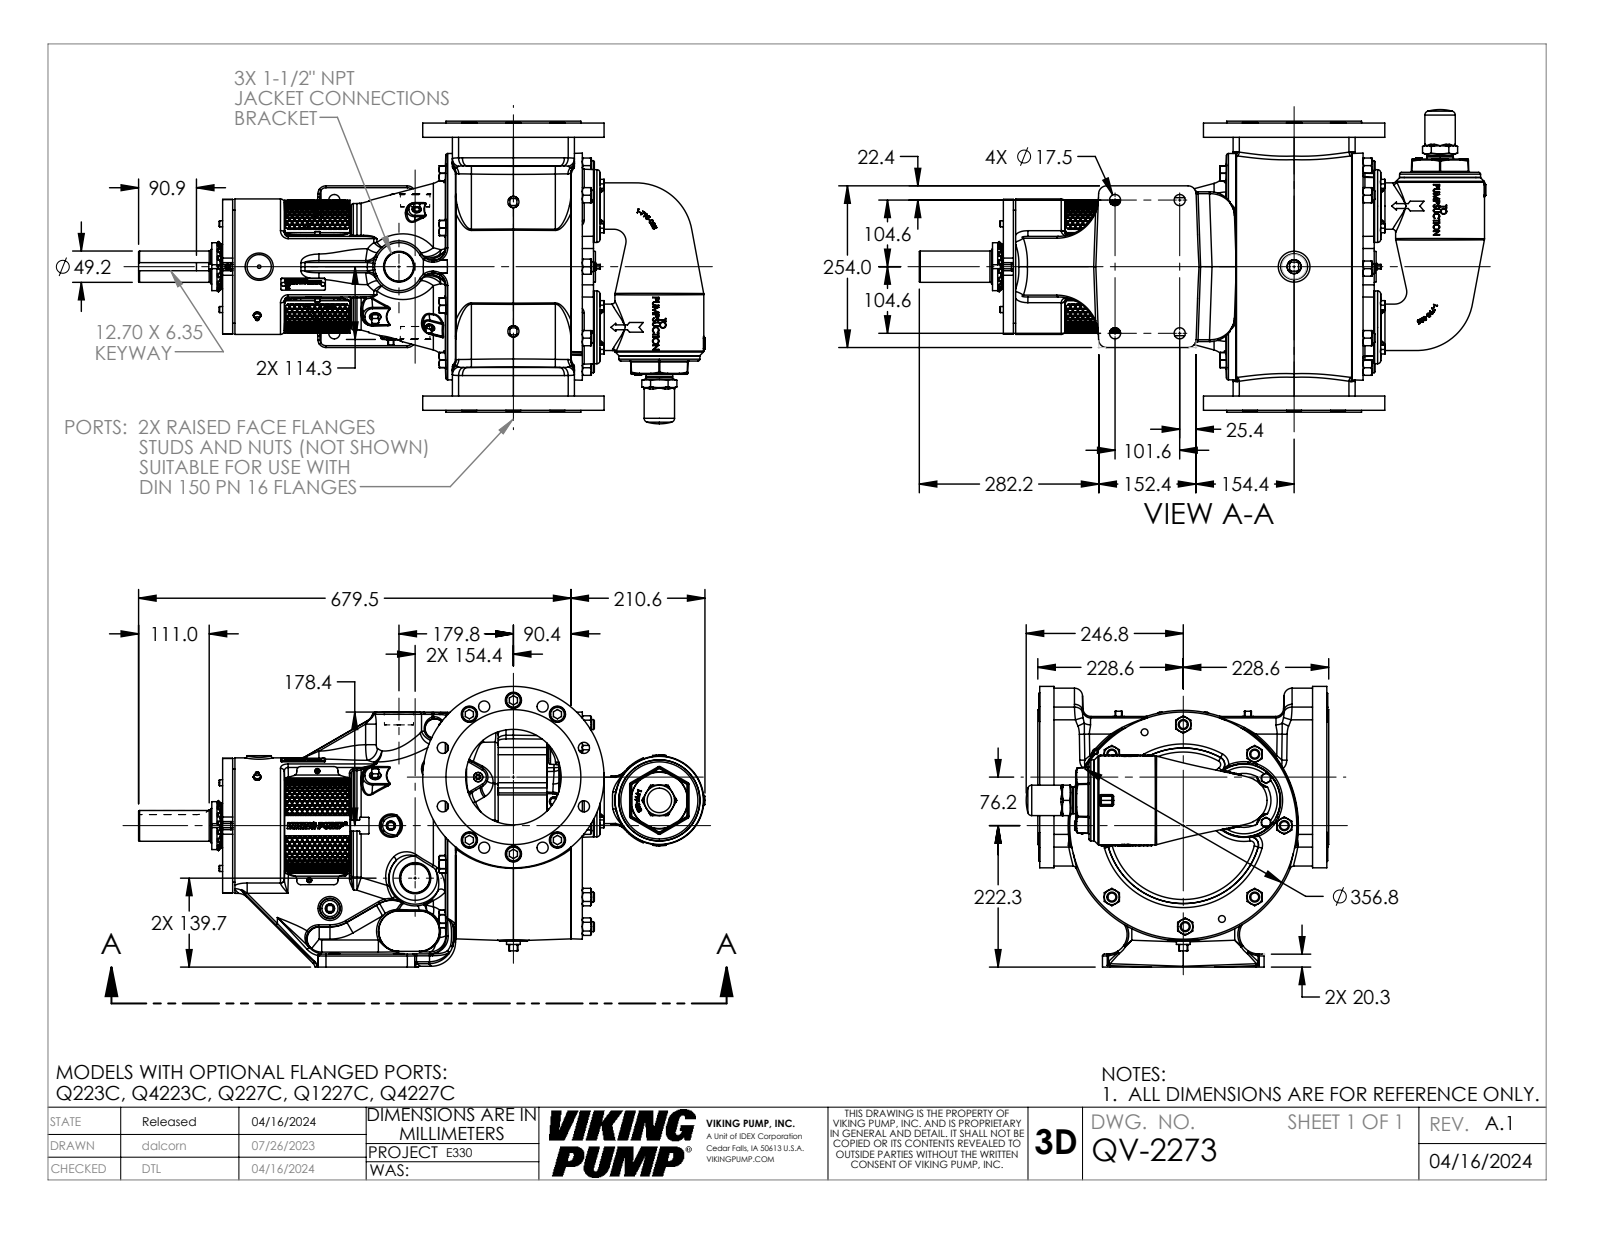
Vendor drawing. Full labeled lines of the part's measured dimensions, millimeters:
Part name (STEP PRODUCT): QV-2273
STEP written by: SolidWorks 2022 (AUTOMOTIVE_DESIGN)
Units: millimetres
Bodies: 1 solid, 8707 faces (3175 planar, 815 cylindrical, 4717 other)
Overall size (bounding box): 890.1 × 475.5 × 440.9
Volume: 46 290 000 mm³ · Surface area: 1 594 000 mm²
Round holes (diameter × count): ⌀6.8 ×8, ⌀10.3 ×8, ⌀17.5 ×8, ⌀29.4 ×8, ⌀6.4 ×6, ⌀16.7 ×6, ⌀25.4 ×6, ⌀17.5 ×4, ⌀4 ×2, ⌀8 ×2, ⌀8.4 ×2, ⌀10.7 ×2
Round bosses / shafts (diameter × count): ⌀9.5 ×9, ⌀15.7 ×8, ⌀23.8 ×6, ⌀15.9 ×5, ⌀11.1 ×3, ⌀7.9 ×3, ⌀114.3 ×2, ⌀15.9 ×2
Partial cylindrical surfaces — rounded edges, fillets, slot ends (radius × count): R3 ×52, R1.5 ×30, R12.7 ×22, R0.4 ×18, R2.3 ×18, R6.4 ×18, R19.1 ×14, R0.8 ×12
Main face-to-face distances: 25.4, 431.8, 457.2, 406.4, 95.3, 12.7, 552.6, 565.3, 457.4, 470.1
Hole centre spacings: 95.3, 120, 52.4, 158.8, 224.5, 293.3, 69, 96.1
